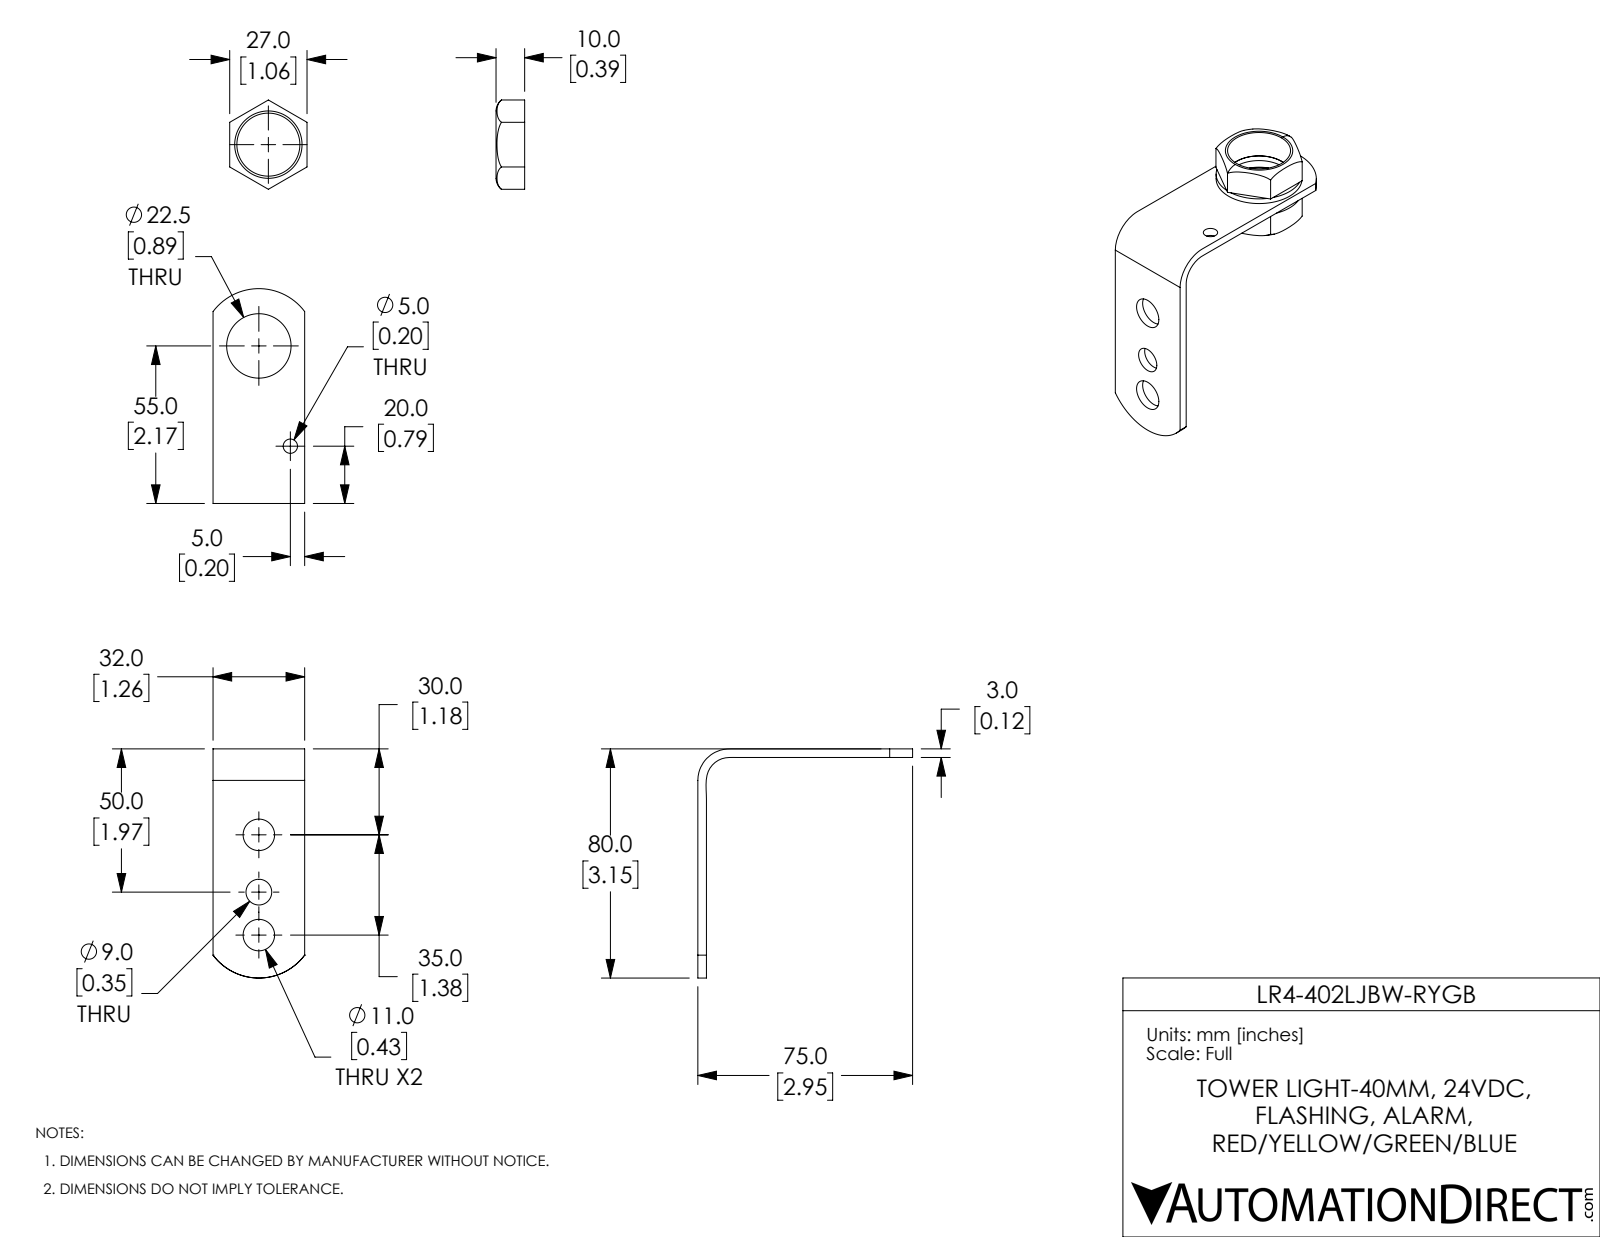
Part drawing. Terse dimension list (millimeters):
name: SZL-001
written by: SolidWorks 2017 (AUTOMOTIVE_DESIGN)
unit: mm
bodies: 5 solids, 54 faces (23 planar, 25 cylindrical, 6 other)
size: 92 × 75 × 32
volume: 17 880 mm³; area: 15 480 mm²
holes: 2× ⌀11, 1× ⌀5, 1× ⌀9, 1× ⌀22, 1× ⌀22.5
bosses: 1× ⌀30
rounds: 2× R20
face distances: 27, 2, 5, 7, 2.5, 29.5, 32, 3, 10, 12
hole spacings: 15, 20, 35, 36.7
